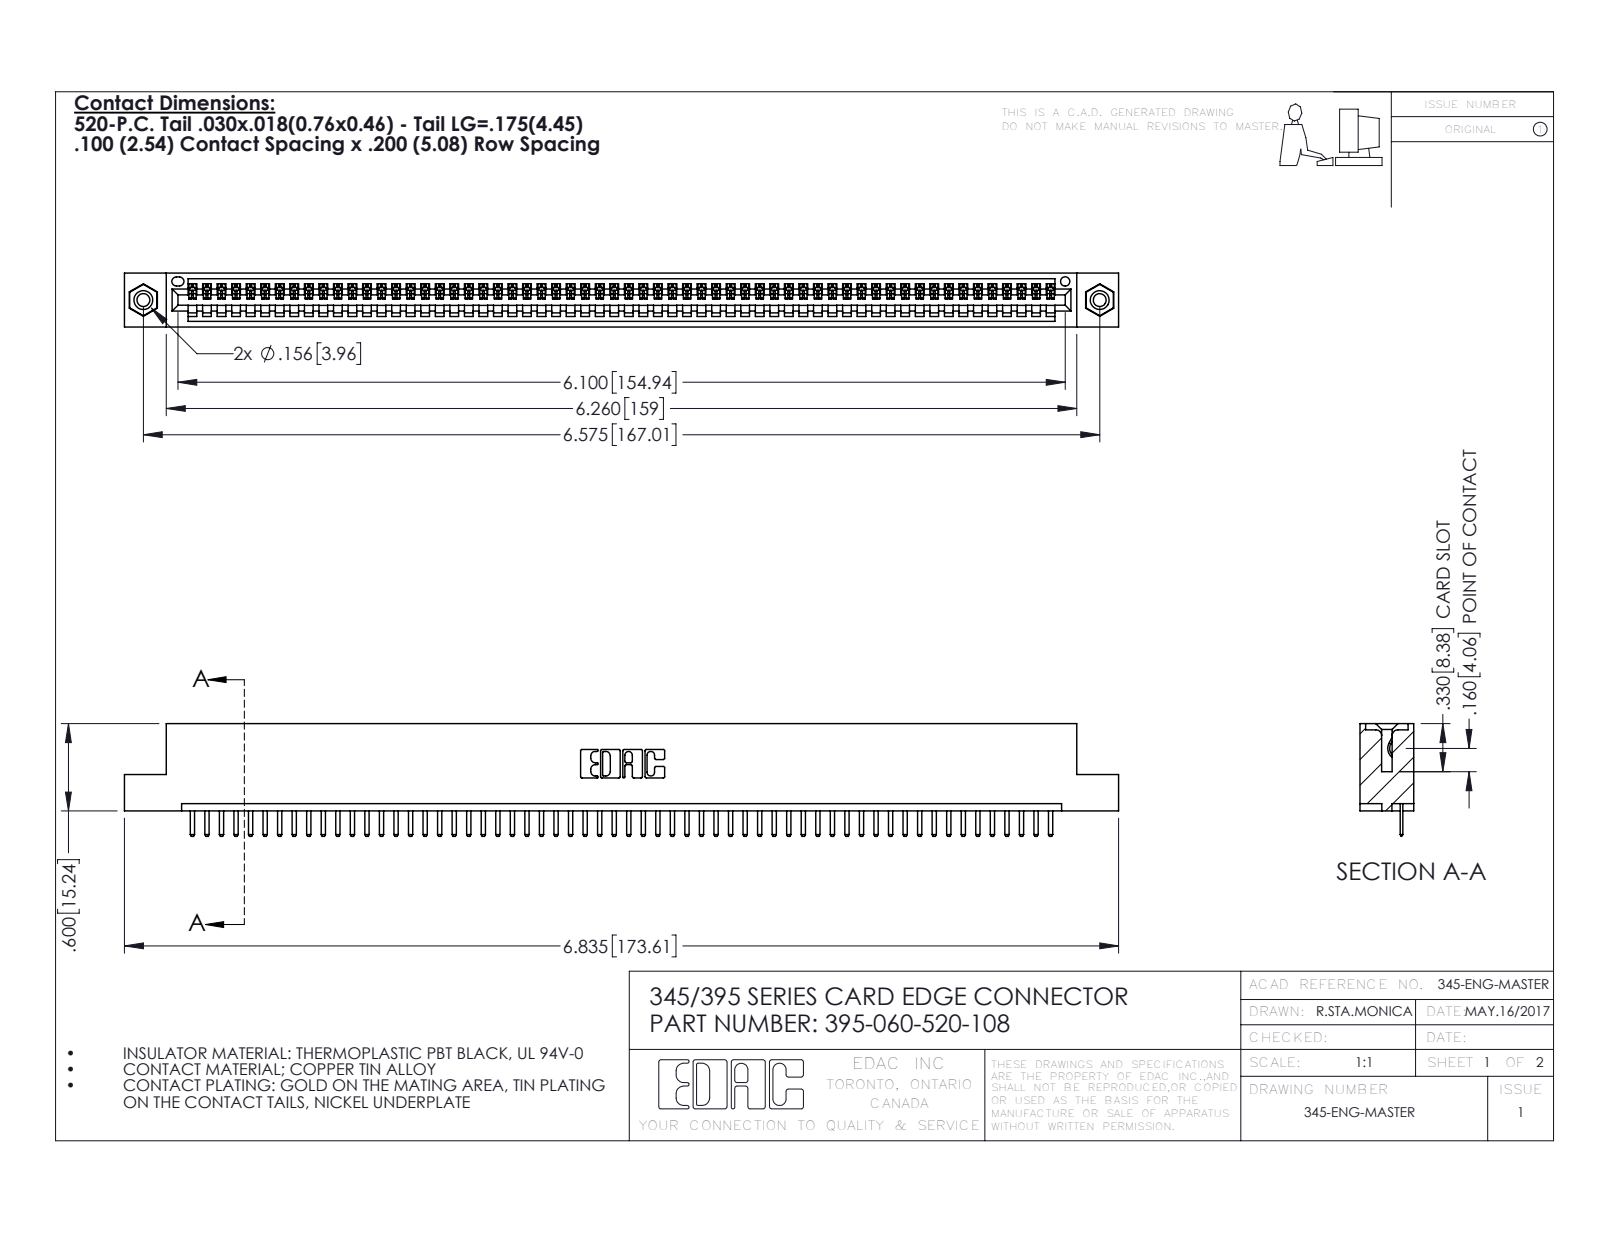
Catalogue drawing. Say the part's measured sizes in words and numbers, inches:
The part is named "345 Part_Flush Mounting Lugs - 0.156 Dia-TI; 345-250-001_345-250-003-102; 345-292-001_345-293-120; 395-060-520-108". Its 3-D file was written by "SolidWorks 2016 (CONFIG_CONTROL_DESIGN)". It is 63 solids with 3906 faces: 2632 planar, 1258 cylindrical and 16 other. Overall it measures 6.835 by 0.775 by 0.37 inches. Its volume is 1.004 cubic inches and its surface area 33.43 square inches. Round holes: 2 of diameter 0.089, 2 of diameter 0.125, 2 of diameter 0.156, 1 of diameter 0.064. Round bosses or shafts: 2 of diameter 0.155. Partial cylindrical surfaces (rounded edges, fillets, slot ends): 122 of radius 0.01, 120 of radius 0.006, 22 of radius 0.01, 6 of radius 0.007, 6 of radius 0.031, 3 of radius 0.026, 2 of radius 0.031, 2 of radius 0.04. The main face-to-face distances are 0.072, 0.298, 0.37, 0.2, 0.098, 0.272, 0.025, 0.225, 0.072, 0.149. The hole center spacings are 0.27, 6.339, 6.575.
